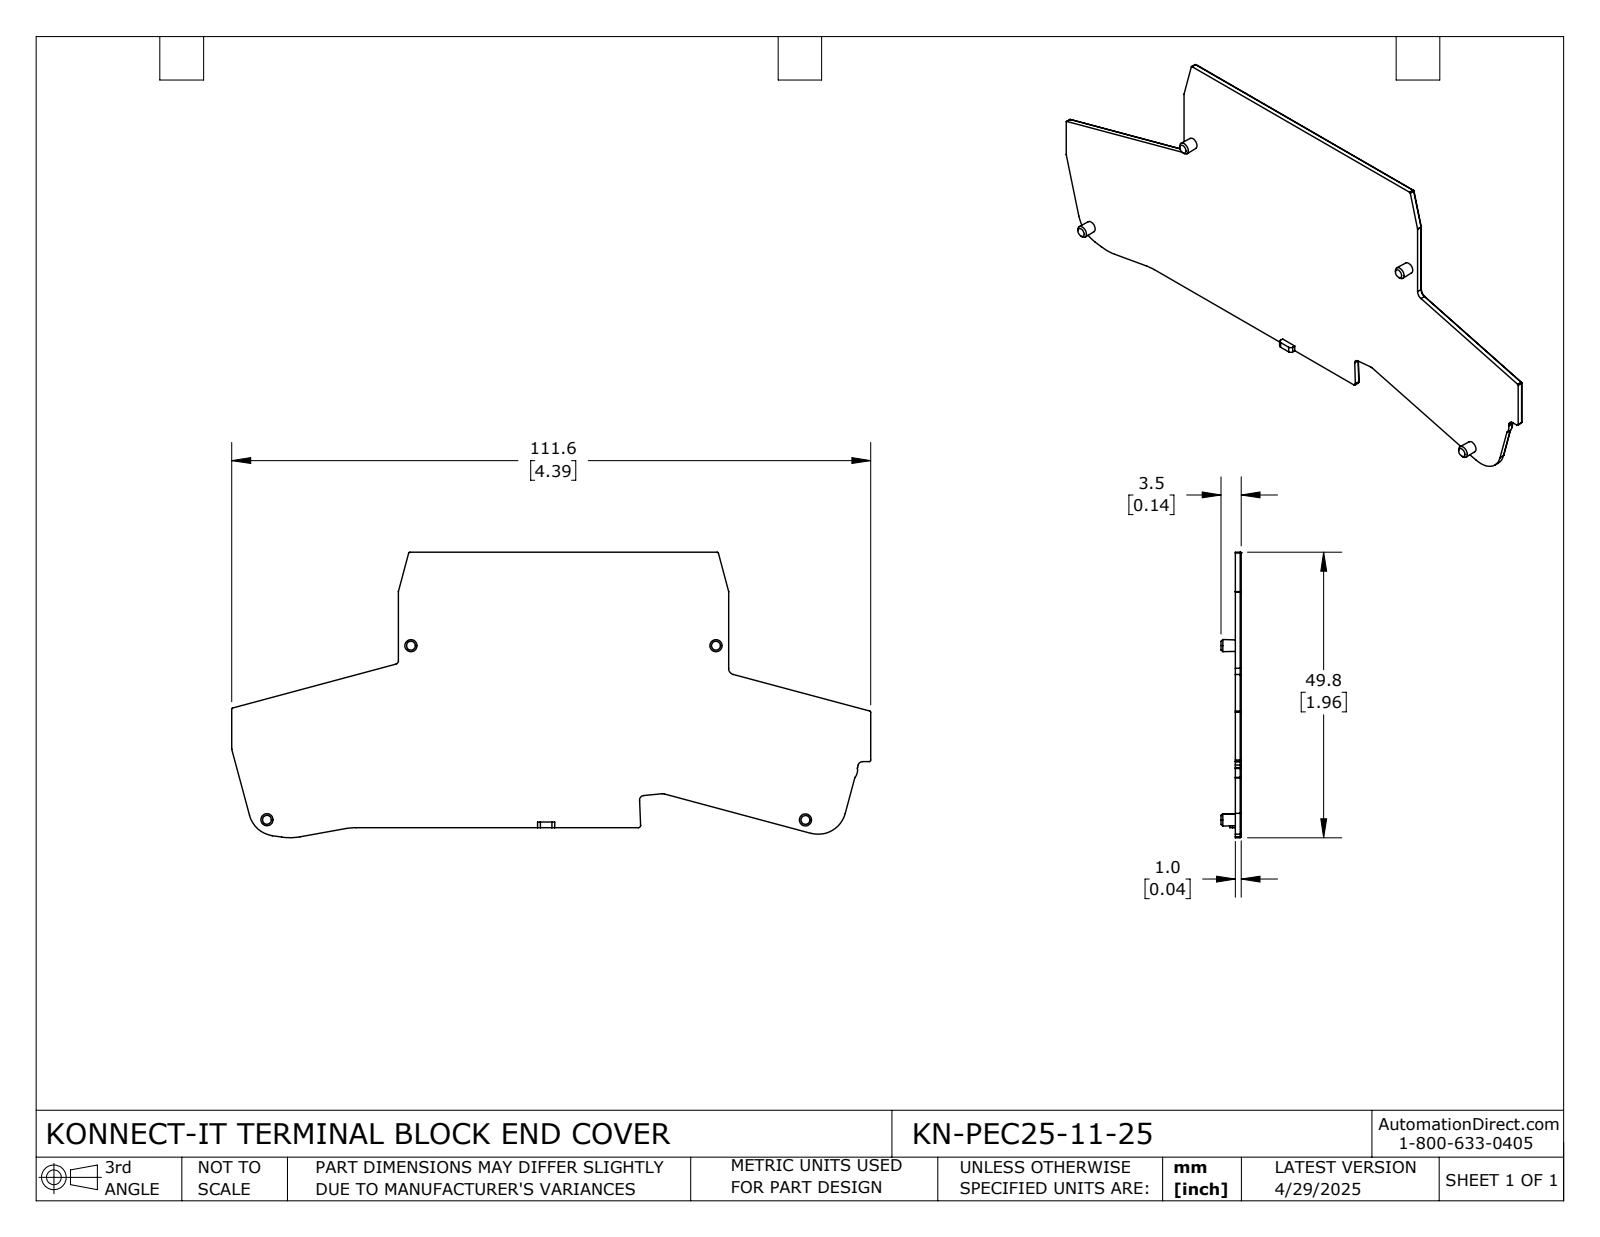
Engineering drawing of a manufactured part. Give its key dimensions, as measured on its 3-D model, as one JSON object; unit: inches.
{"part_name": "KN-PEC25-11-25", "step_written_by": "SolidWorks 2024 (CONFIG_CONTROL_DESIGN)", "units": "inches", "bodies": {"solids": 1, "faces": 117, "planar": 51, "cylindrical": 50, "other": 16}, "overall_size": [4.393, 1.962, 0.138], "volume_in3": 0.242, "surface_area_in2": 12.77, "partial_cylinders_radius": [[0.008, 8], [0.004, 7], [0.012, 4], [0.016, 3], [0.02, 2], [0.043, 2], [0.047, 2], [0.189, 2]], "face_to_face_distances": [0.039, 1.893, 0.033, 0.916, 1.889, 2.271, 0.977, 0.912, 0.098, 0.132]}
